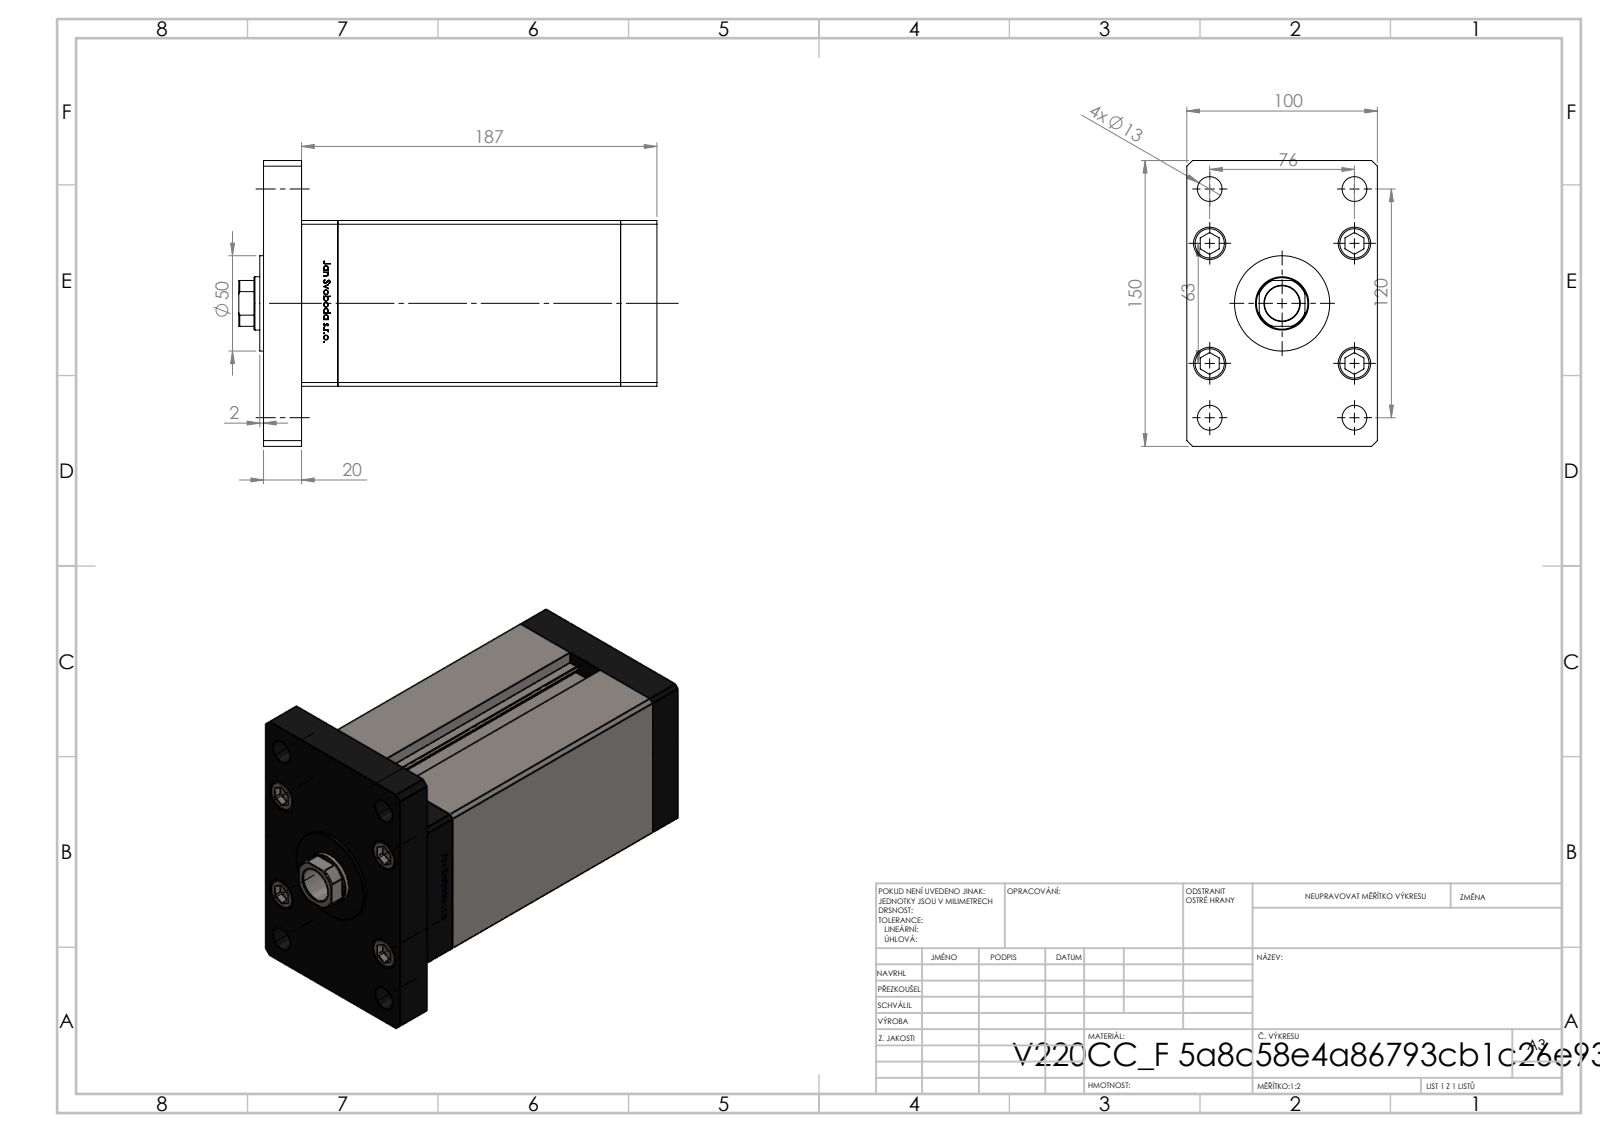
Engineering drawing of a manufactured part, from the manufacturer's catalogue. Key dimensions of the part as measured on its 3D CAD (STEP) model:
Part name (STEP PRODUCT): ALLEN BOLT; V220C_F; V220C_FRONT_F; V220C_F_MIDDLE (+2 more)
STEP written by: SolidWorks 2019 (CONFIG_CONTROL_DESIGN)
Units: millimetres
Bodies: 19 solids, 1311 faces (517 planar, 188 cylindrical, 606 other)
Overall size (bounding box): 219.5 × 150 × 100
Volume: 1 705 000 mm³ · Surface area: 259 381 mm²
Round holes (diameter × count): ⌀13.5 ×7, ⌀18 ×7, ⌀12 ×4, ⌀13 ×4, ⌀17 ×4, ⌀2 ×2, ⌀13.16 ×2, ⌀18.5 ×1, ⌀28 ×1, ⌀29.5 ×1
Round bosses / shafts (diameter × count): ⌀8 ×9, ⌀17 ×5, ⌀50 ×1
Partial cylindrical surfaces — rounded edges, fillets, slot ends (radius × count): R0.93 ×2, R13.5 ×1
Main face-to-face distances: 19, 167.5, 100, 87, 20, 148.5, 39, 187.5, 186.5, 206.5
Hole centre spacings: 34, 18.59, 28.5, 37.13, 39.64, 49.36, 57.95, 71.02
